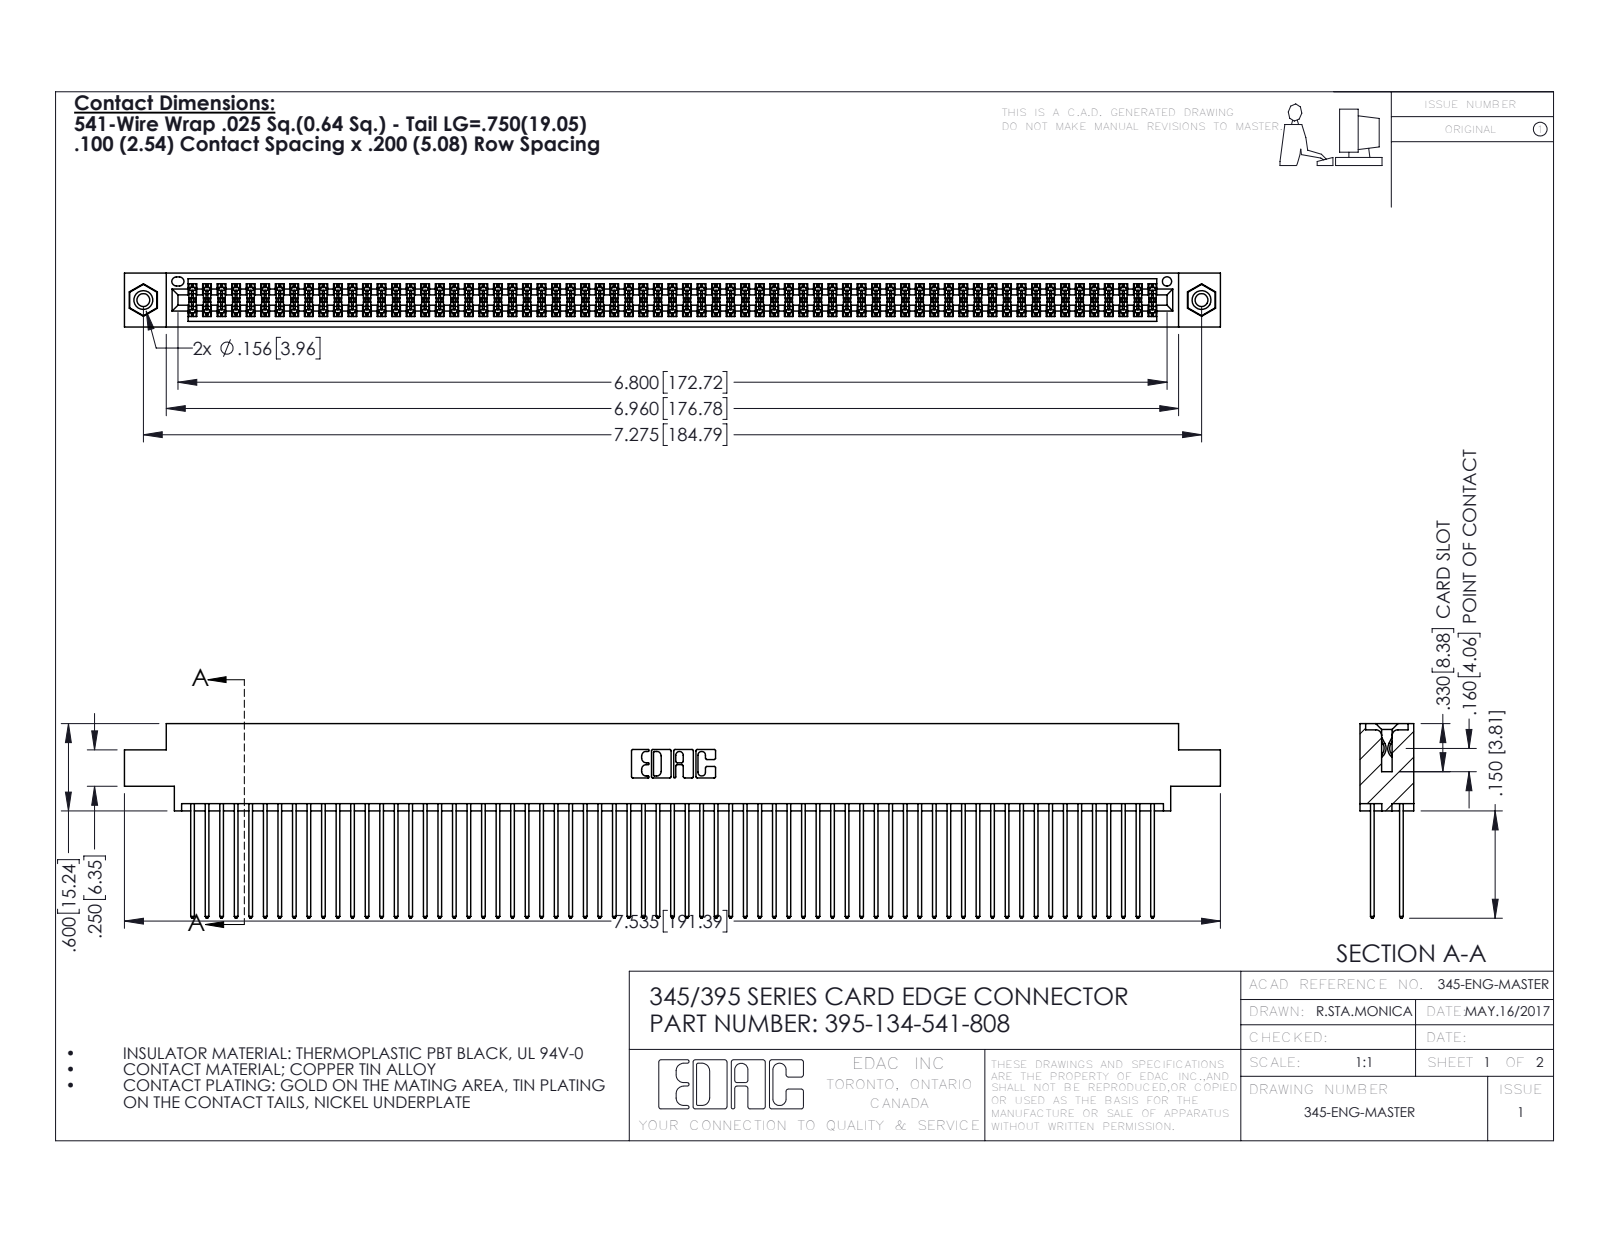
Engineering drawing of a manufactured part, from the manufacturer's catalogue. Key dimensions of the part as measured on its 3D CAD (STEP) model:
Part name (STEP PRODUCT): 395-134-541-808; 345 Part_0.170 Offset - 0.156 Dia-TI; 345-292-001_345-293-141; 345-250-001_345-250-003-102
STEP written by: SolidWorks 2016 (CONFIG_CONTROL_DESIGN)
Units: inches
Bodies: 137 solids, 6890 faces (4538 planar, 2336 cylindrical, 16 other)
Overall size (bounding box): 7.535 × 1.337 × 0.37
Volume: 1.188 in³ · Surface area: 51.21 in²
Round holes (diameter × count): ⌀0.089 ×2, ⌀0.125 ×2, ⌀0.156 ×2, ⌀0.064 ×1
Round bosses / shafts (diameter × count): ⌀0.155 ×2
Partial cylindrical surfaces — rounded edges, fillets, slot ends (radius × count): R0.006 ×201, R0.01 ×134, R0.01 ×22, R0.007 ×6, R0.031 ×6, R0.026 ×3, R0.014 ×2, R0.019 ×2
Main face-to-face distances: 0.072, 0.298, 0.2, 0.098, 0.272, 0.025, 0.225, 0.37, 0.175, 0.149
Hole centre spacings: 0.27, 7.039, 7.275
